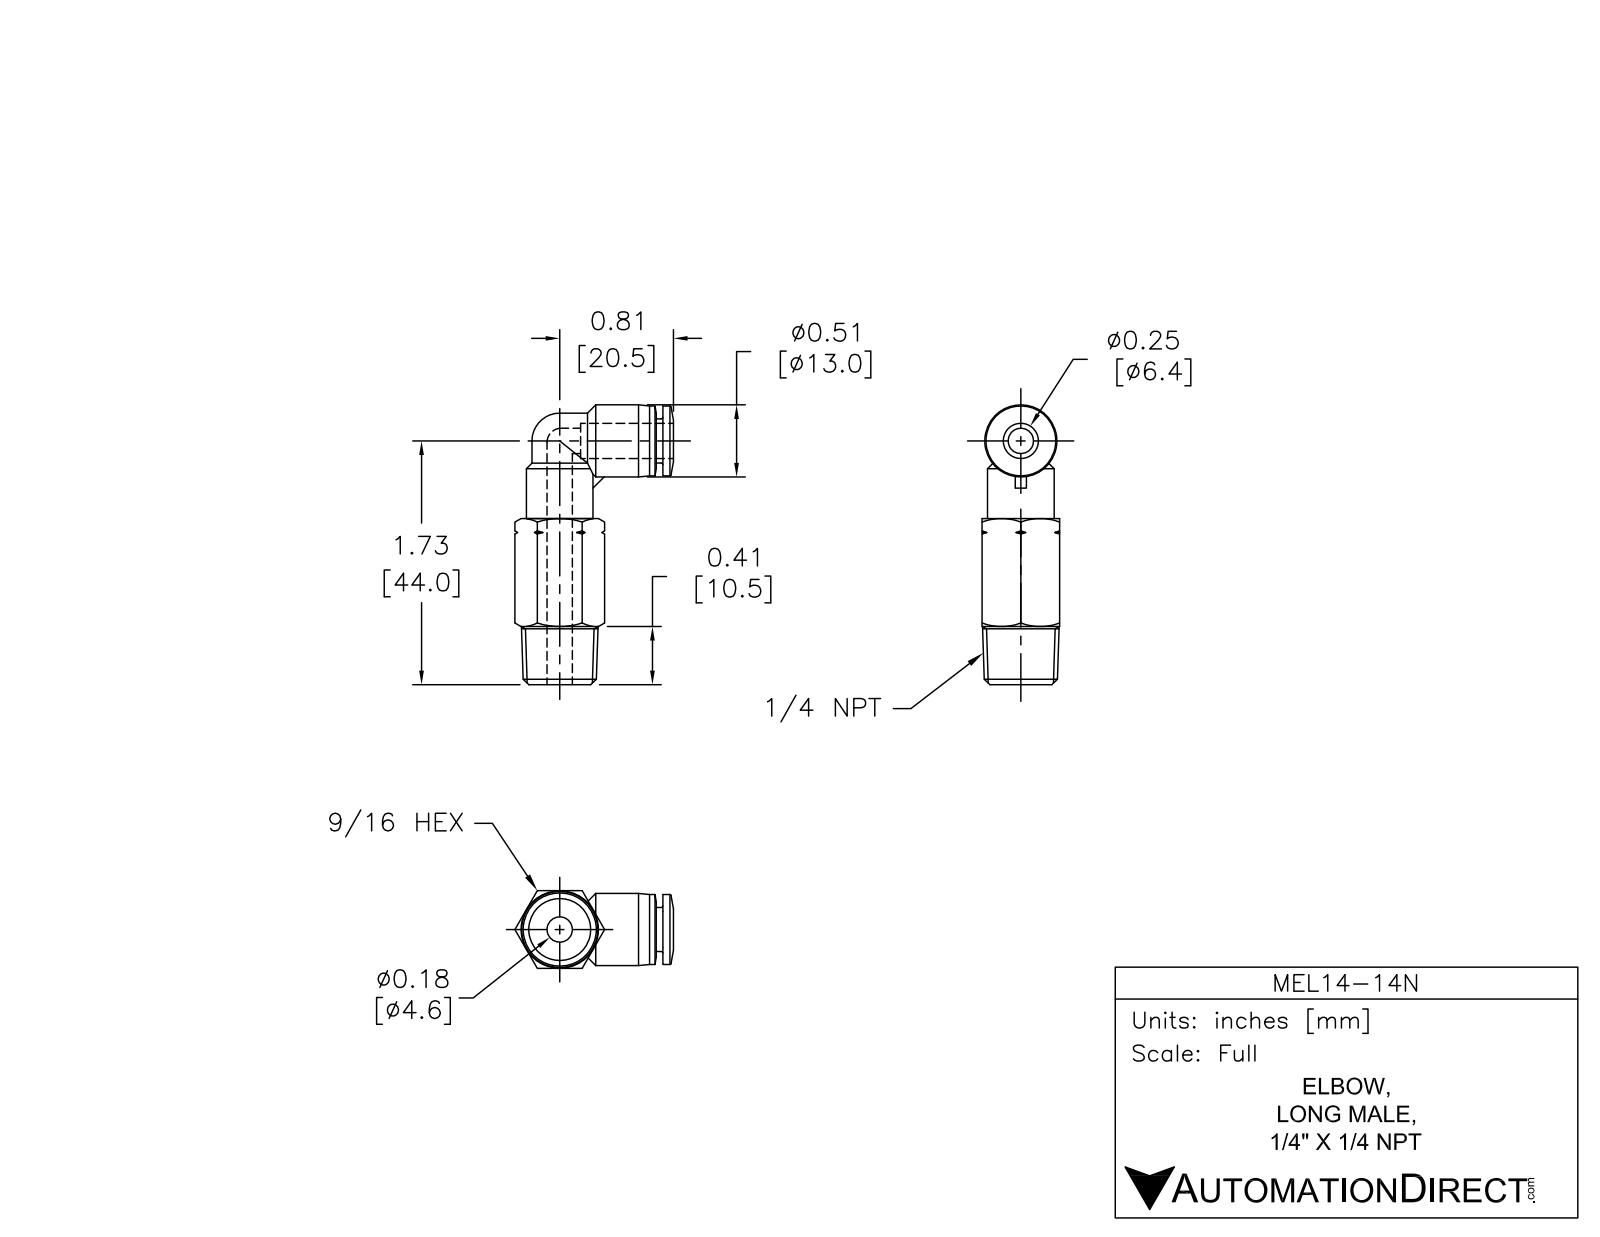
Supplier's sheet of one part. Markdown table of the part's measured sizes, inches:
| quantity | value |
| --- | --- |
| part name | MEL14-14N |
| STEP written by | SolidWorks 2015 (AUTOMOTIVE_DESIGN) |
| units | inches |
| bodies | 1 solid, 88 faces (15 planar, 20 cylindrical, 53 other) |
| overall size | 1.988 × 1.125 × 0.551 |
| volume | 0.433 in³ |
| surface area | 6.278 in² |
| round holes (diameter × count) | 0.177 × 2, 0.258 × 1 |
| round bosses / shafts (diameter × count) | 0.394 × 2, 0.512 × 1, 0.496 × 1, 0.472 × 1, 0.313 × 1 |
| main face-to-face distances | 0.551, 1.181, 0.047, 0.539, 0.587, 0.236, 0.315, 0.413, 0.768, 0.079 |
